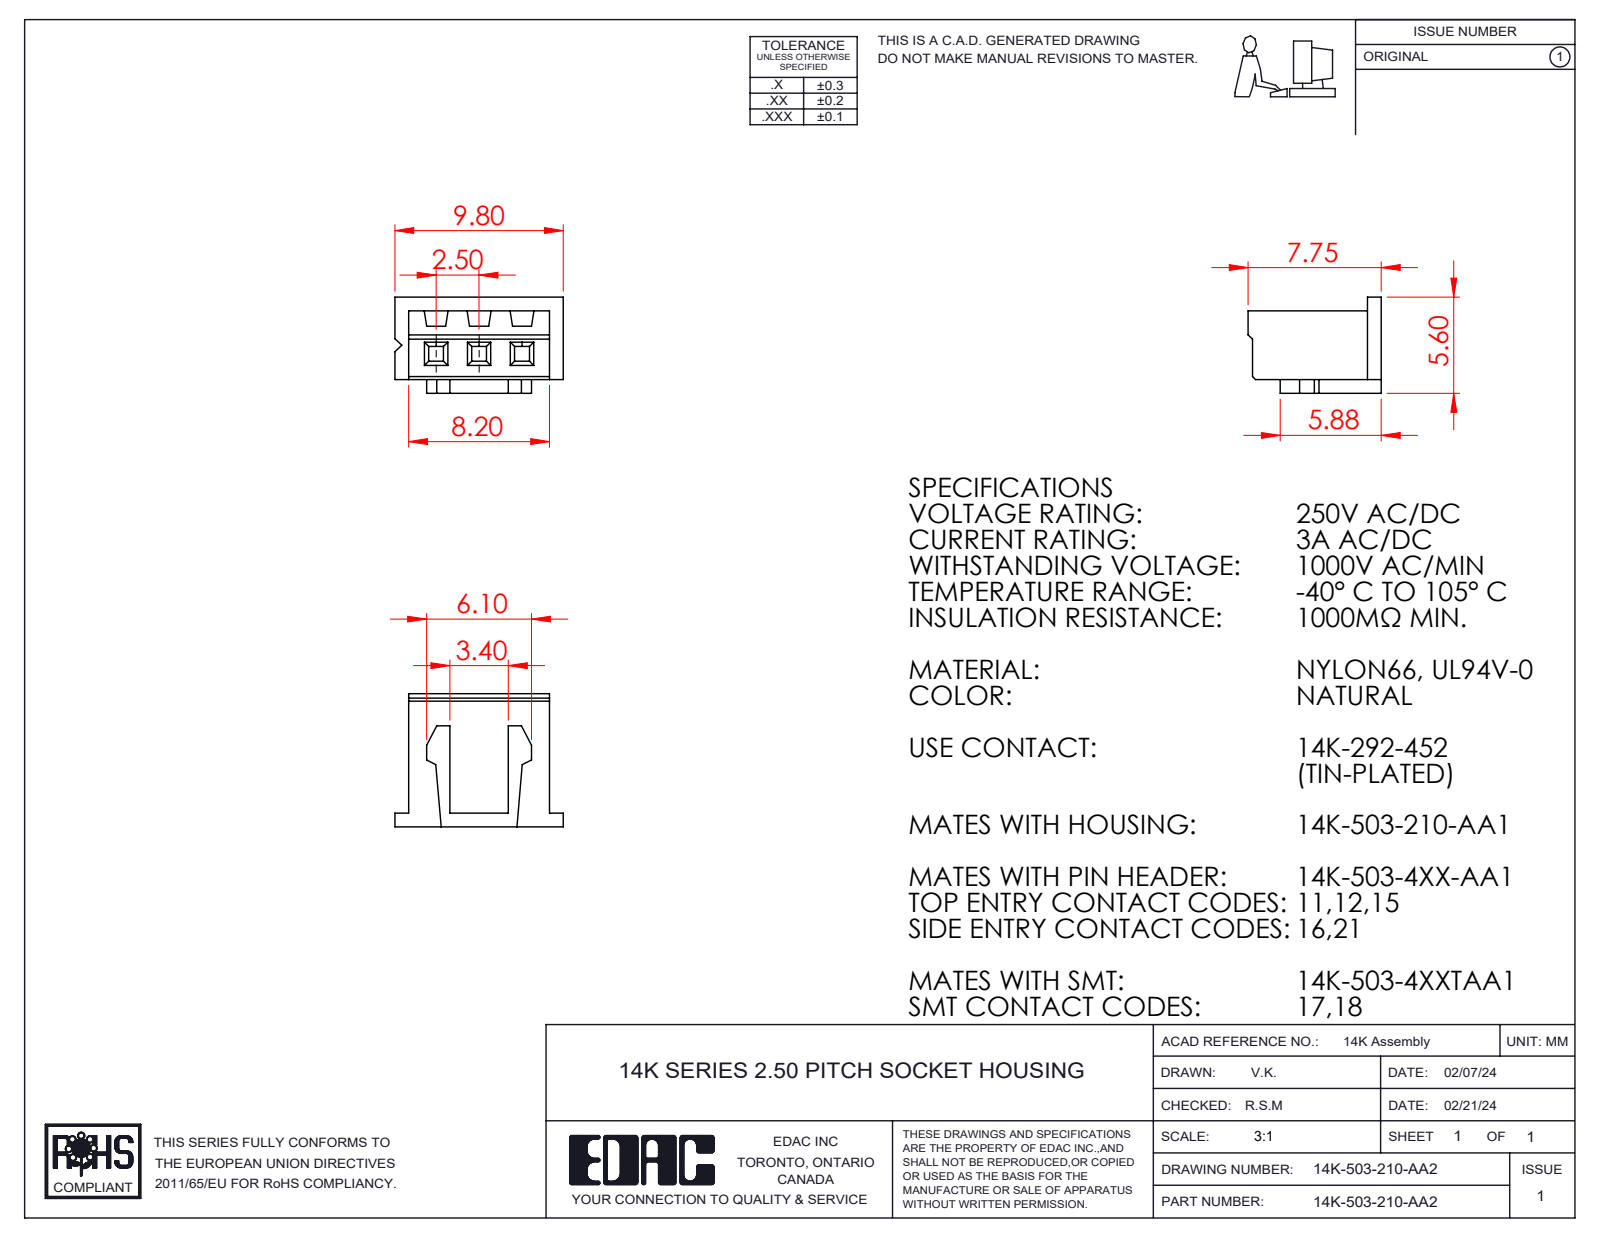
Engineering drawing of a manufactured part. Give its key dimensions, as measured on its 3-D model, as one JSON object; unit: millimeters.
{"part_name": "14K-503-210-AA2", "step_written_by": "SolidWorks 2023 (CONFIG_CONTROL_DESIGN)", "units": "millimeters", "bodies": {"solids": 1, "faces": 96, "planar": 96, "cylindrical": 0, "other": 0}, "overall_size": [9.8, 7.75, 5.6], "volume_mm3": 145, "surface_area_mm2": 509, "face_to_face_distances": [2.5, 2.1, 0.8, 4, 3.38, 0.62, 5, 0.55, 2.65, 3.05]}
